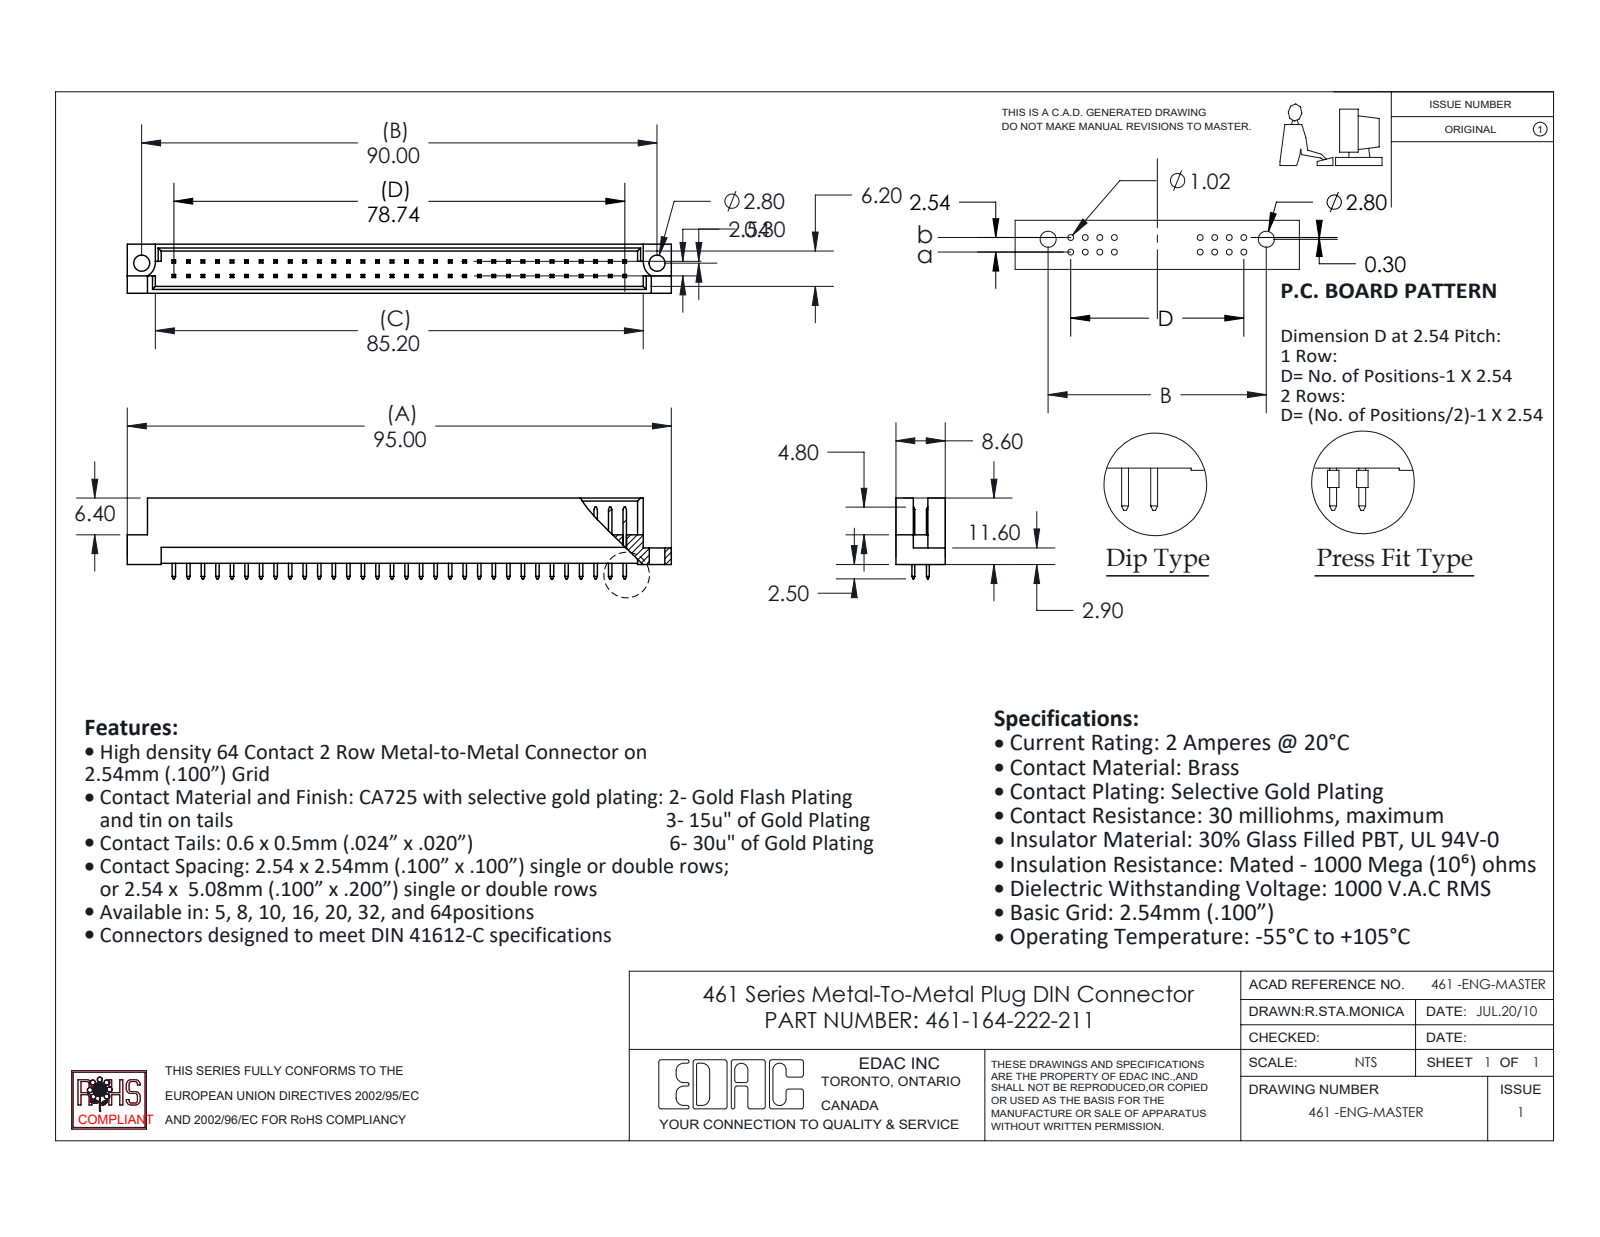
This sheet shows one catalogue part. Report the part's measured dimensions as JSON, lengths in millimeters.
{"part_name": "461-290_22; 461-164-222-211; 461 Part_64", "step_written_by": "SolidWorks 2020 (CONFIG_CONTROL_DESIGN)", "units": "millimeters", "bodies": {"solids": 65, "faces": 1201, "planar": 1194, "cylindrical": 7, "other": 0}, "overall_size": [95, 14.1, 8.6], "volume_mm3": 4889, "surface_area_mm2": 7407, "round_holes": [[2.8, 2]], "partial_cylinders_radius": [[2.8, 2]], "face_to_face_distances": [1.2, 7.4, 8.6, 2.54, 6.2, 3.28, 5.32, 2.08, 4.12, 2.78], "hole_center_spacings": [90]}
